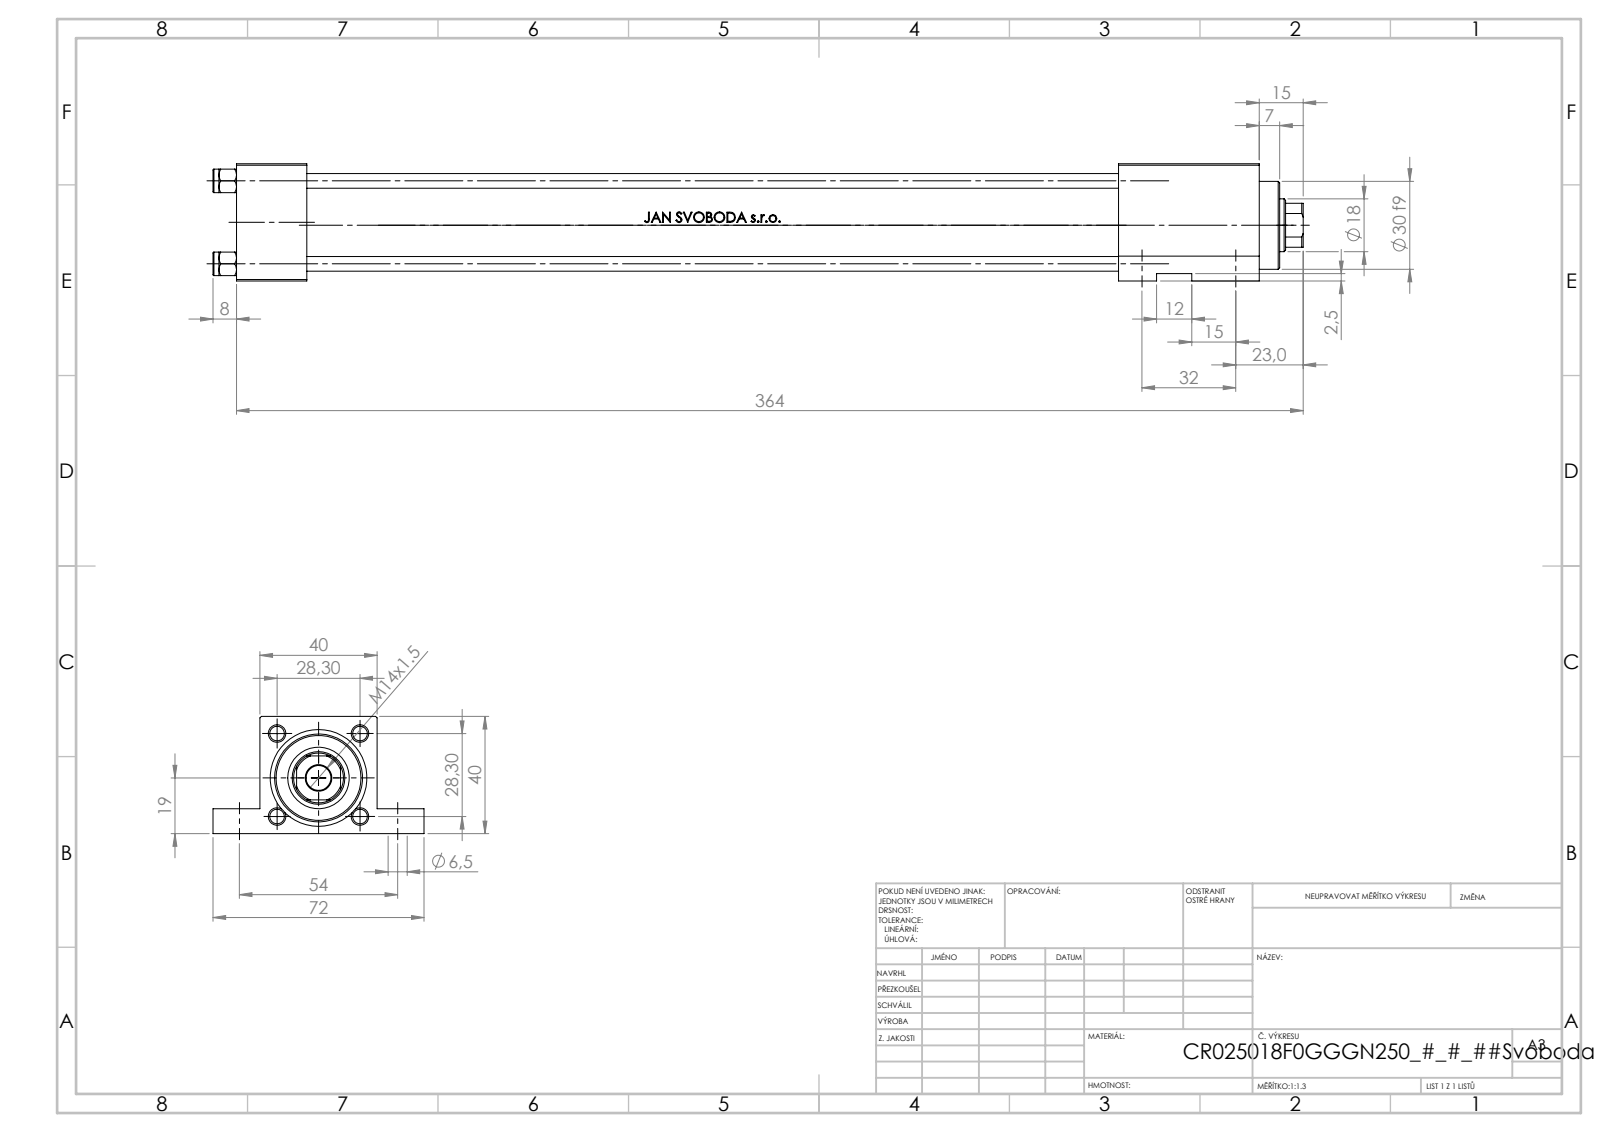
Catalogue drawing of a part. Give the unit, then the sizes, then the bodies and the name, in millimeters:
Units: millimetres
Overall size (bounding box): 372 × 72 × 40
Round holes (diameter × count): ⌀5 ×4, ⌀6.5 ×4, ⌀20 ×3, ⌀7 ×2, ⌀13.16 ×2, ⌀8.5 ×1, ⌀18 ×1, ⌀21 ×1, ⌀25 ×1, ⌀30 ×1
Round bosses / shafts (diameter × count): ⌀8 ×4, ⌀31 ×1
Partial cylindrical surfaces — rounded edges, fillets, slot ends (radius × count): R8.5 ×1
Main face-to-face distances: 40, 24, 8.5, 31.5, 301, 277, 48, 6, 349, 325
Hole centre spacings: 28.3, 19.32, 20.73, 27.46, 32, 38.18, 40.02, 54
Volume: 296 931 mm³ · Surface area: 128 845 mm²
Bodies: 11 solids, 1100 faces (436 planar, 124 cylindrical, 540 other)
Part name (STEP PRODUCT): V215CR_F_TYCINKA; V215CR_F_Body; NUT_M5_F; V215CR_VCP_F (+1 more)
STEP written by: SolidWorks 2019 (CONFIG_CONTROL_DESIGN)
